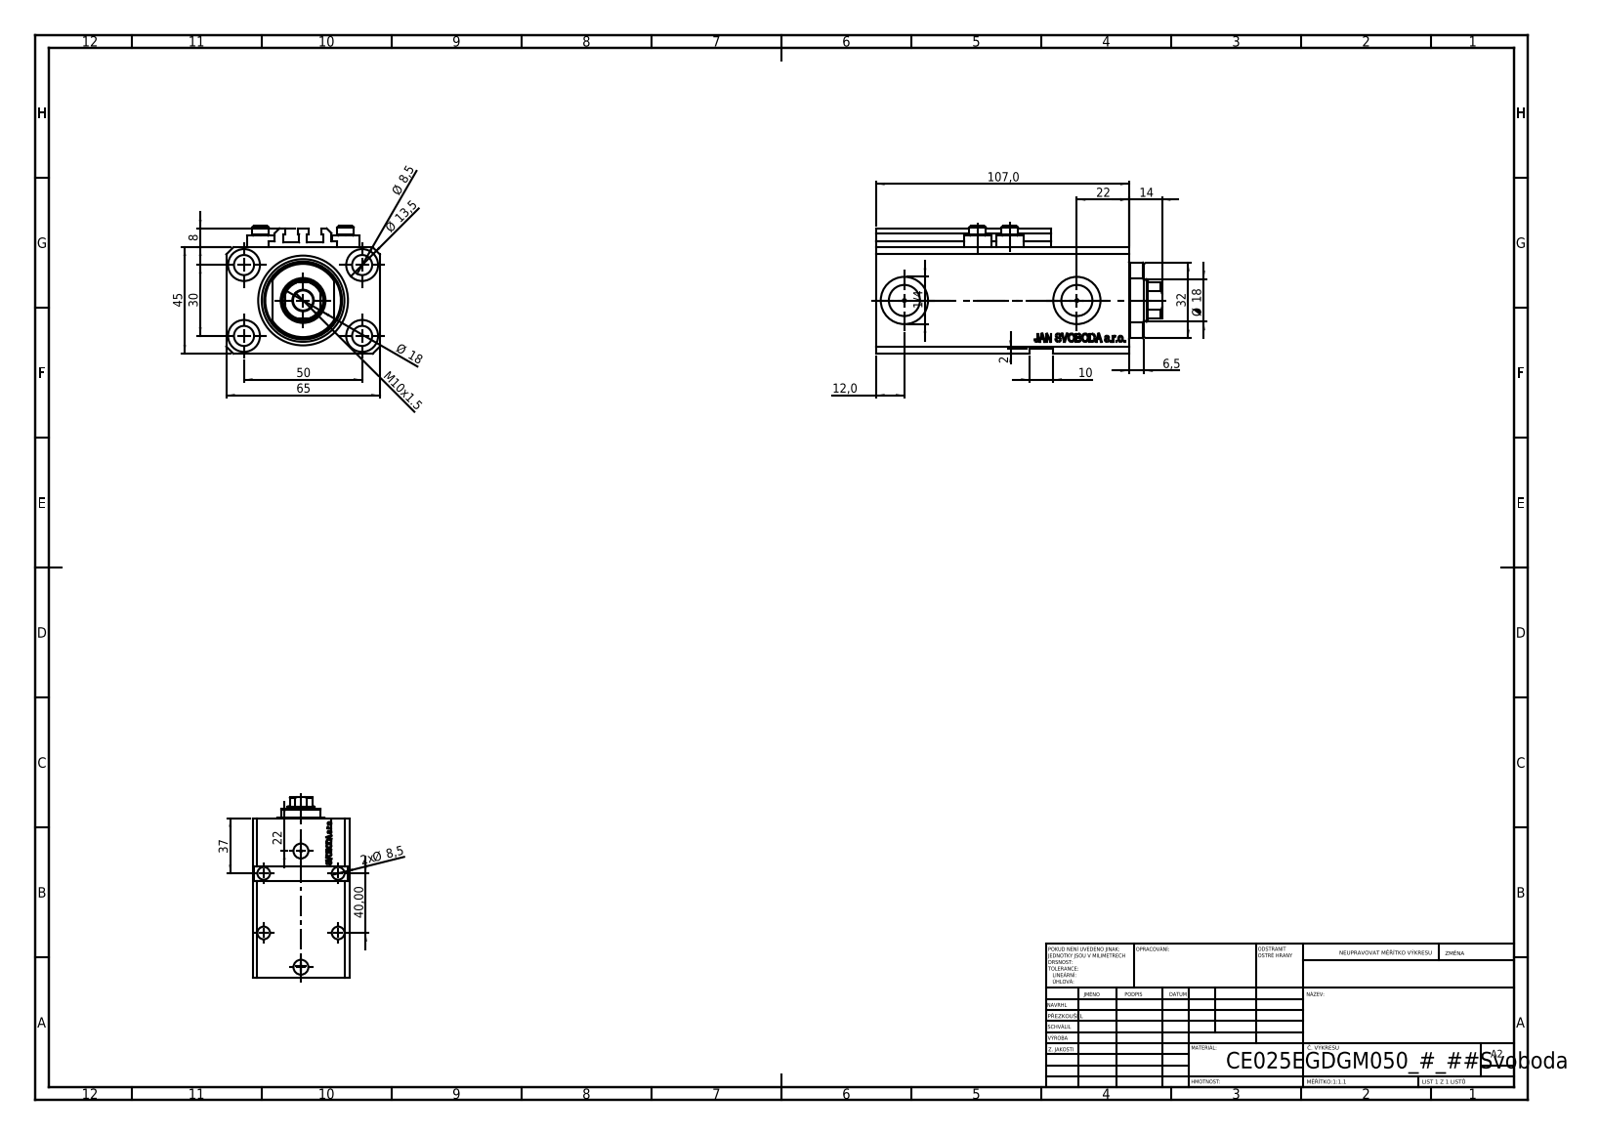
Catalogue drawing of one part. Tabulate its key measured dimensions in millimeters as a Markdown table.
| quantity | value |
| --- | --- |
| part name | V250CE_E_Body; V250CE_C_VCP; V250CE_VC_E; ALLEN BOLT V250CE |
| STEP written by | SolidWorks 2019 (CONFIG_CONTROL_DESIGN) |
| units | millimeters |
| bodies | 8 solids, 1103 faces (515 planar, 158 cylindrical, 430 other) |
| overall size | 121 × 65 × 54 |
| volume | 269 783 mm³ |
| surface area | 78 013 mm² |
| round holes (diameter × count) | 8.5 × 9, 1.25 × 4, 4 × 4, 13.5 × 4, 10 × 2, 13.16 × 2, 20 × 2, 18 × 1, 25 × 1, 38 × 1 |
| round bosses / shafts (diameter × count) | 11.6 × 4, 7 × 4 |
| partial cylindrical surfaces (radius × count) | 0.2 × 10, 8.5 × 1, 16 × 1 |
| main face-to-face distances | 45, 65, 93, 2, 14, 47, 107, 2.5, 10, 6.9 |
| hole center spacings | 29.15, 50, 13.6, 14.76, 15.12, 27.51, 27.89, 30 |
